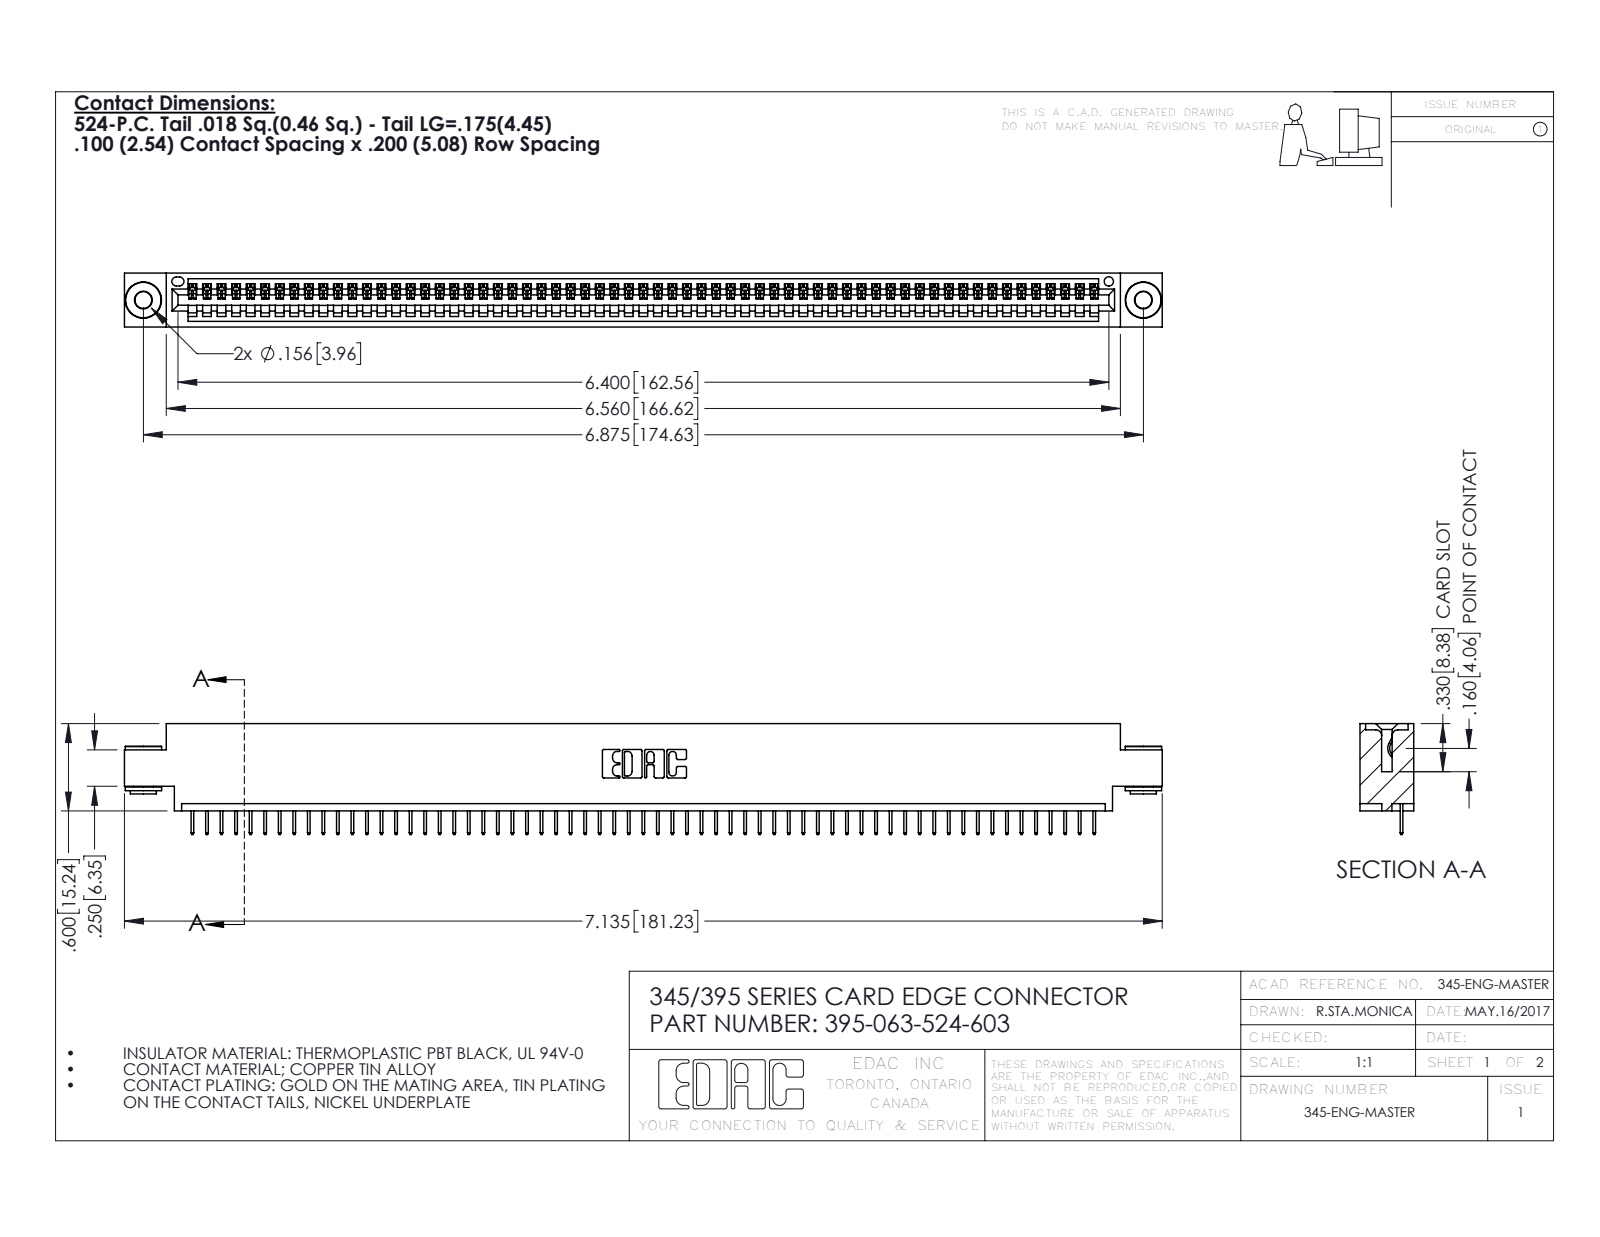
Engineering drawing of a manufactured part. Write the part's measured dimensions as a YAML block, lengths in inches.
part_name: "345 Part_0.170 Offset - 0.156 Dia-TH; 395-063-524-603; 345-292-001_345-293-124; 345-250-002_345-250-002-102"
step_written_by: "SolidWorks 2016 (CONFIG_CONTROL_DESIGN)"
units: inches
bodies: {solids: 66, faces: 4074, planar: 2992, cylindrical: 1074, other: 8}
overall_size: [7.135, 0.762, 0.37]
volume: 1.04
surface_area: 34.84
round_holes:
  - {diameter: 0.116, count: 2}
  - {diameter: 0.156, count: 2}
  - {diameter: 0.064, count: 1}
round_bosses_or_shafts:
  - {diameter: 0.25, count: 2}
  - {diameter: 0.18, count: 2}
  - {diameter: 0.136, count: 2}
partial_cylinders:
  - {radius: 0.006, count: 126}
  - {radius: 0.01, count: 22}
  - {radius: 0.007, count: 6}
  - {radius: 0.031, count: 6}
  - {radius: 0.026, count: 3}
  - {radius: 0.031, count: 2}
  - {radius: 0.04, count: 2}
  - {radius: 0.014, count: 1}
face_to_face_distances: [0.072, 0.298, 0.37, 0.2, 0.098, 0.272, 0.025, 0.225, 0.072, 0.175]
hole_center_spacings: [0.27, 6.639, 6.875]
